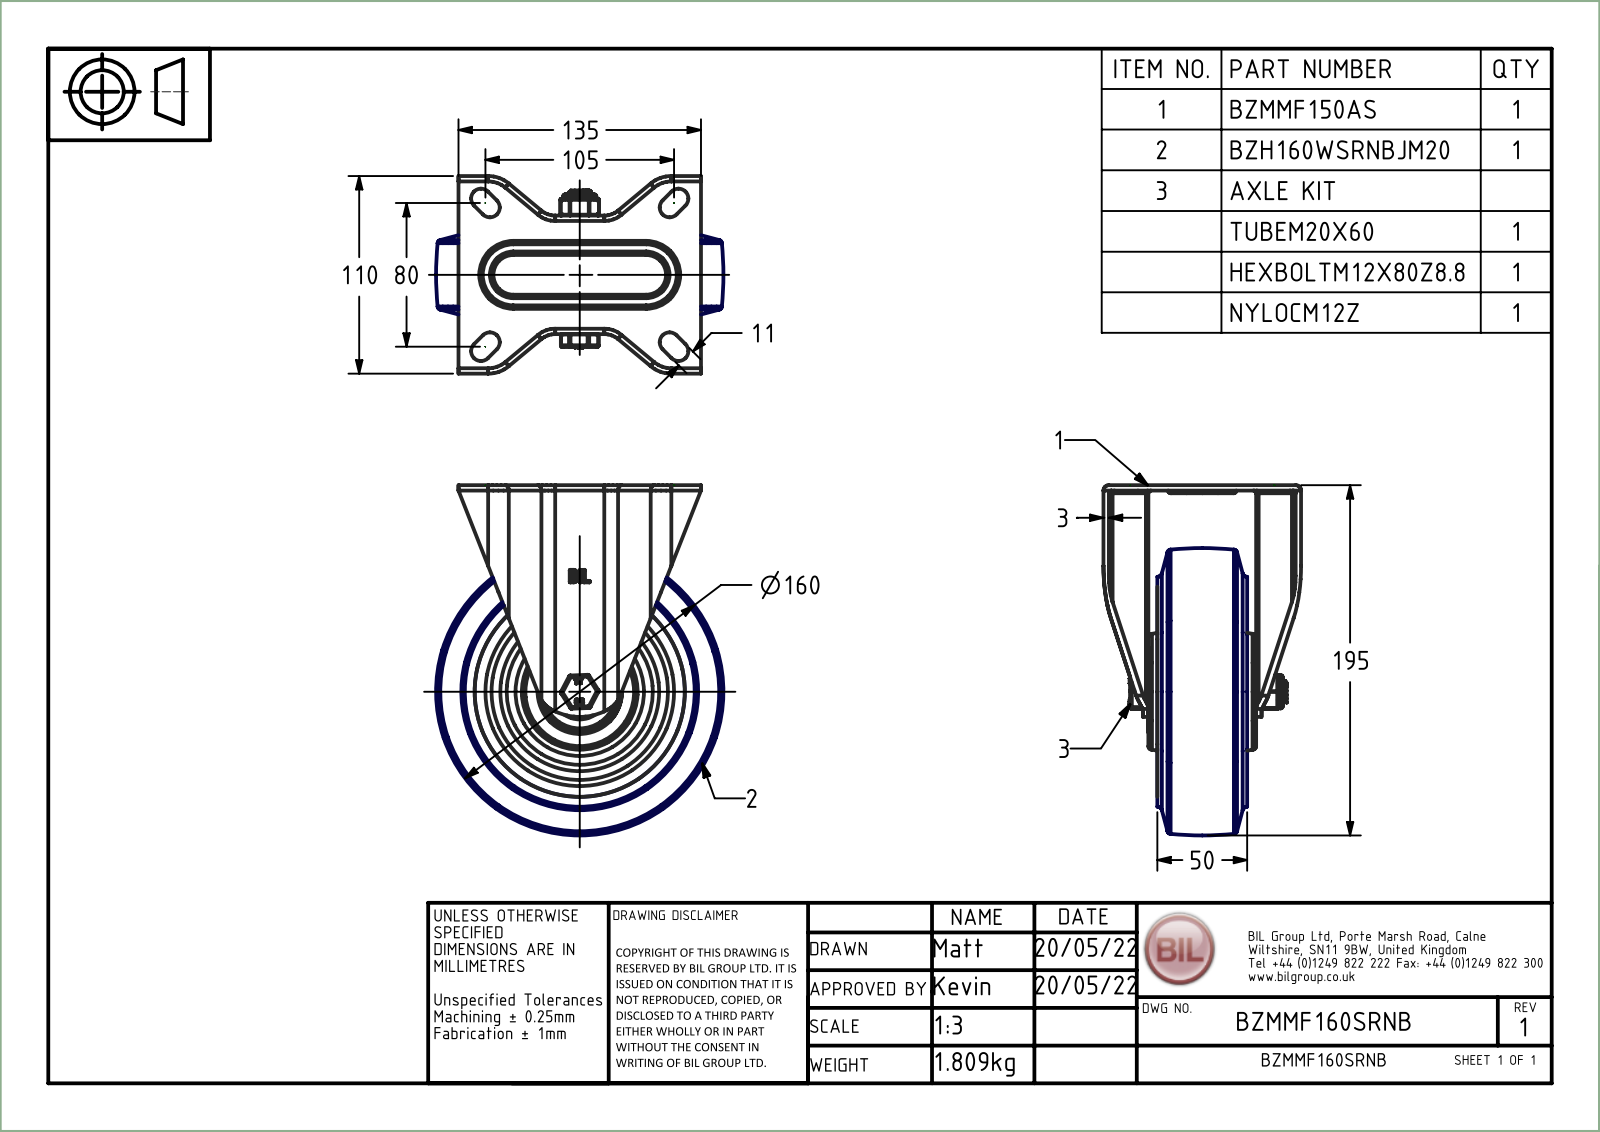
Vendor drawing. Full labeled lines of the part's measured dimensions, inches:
Part name (STEP PRODUCT): BZMMF150AS; BZMMF150AS Geometry; ZINC PLATED, PRESSED STEEL BRACKET; BZMMF160SRNB (+8 more)
STEP written by: Spatial InterOp 3D (AUTOMOTIVE_DESIGN)
Units: inches
Bodies: 34 solids, 1353 faces (419 planar, 374 cylindrical, 560 other)
Overall size (bounding box): 7.677 × 6.299 × 4.331
Volume: 53.56 in³ · Surface area: 377.8 in²
Round holes (diameter × count): ⌀0.472 ×1, ⌀0.482 ×1, ⌀0.492 ×1, ⌀0.551 ×1, ⌀0.787 ×1, ⌀1.122 ×1, ⌀1.213 ×1, ⌀1.575 ×1, ⌀1.587 ×1, ⌀1.594 ×1, ⌀1.654 ×1, ⌀1.85 ×1
Round bosses / shafts (diameter × count): ⌀1.606 ×1, ⌀1.232 ×1, ⌀1.063 ×1, ⌀0.945 ×1, ⌀0.783 ×1, ⌀0.728 ×1, ⌀0.709 ×1, ⌀0.394 ×1
Partial cylindrical surfaces — rounded edges, fillets, slot ends (radius × count): R0.02 ×18, R0.039 ×12, R0.059 ×12, R0.118 ×8, R0.217 ×8, R0.079 ×4, R0.236 ×4, R0.354 ×4
Main face-to-face distances: 0.118, 0.974, 0.197, 2.165, 2.362, 0.315, 2.283, 2.48, 1.969, 0.856
